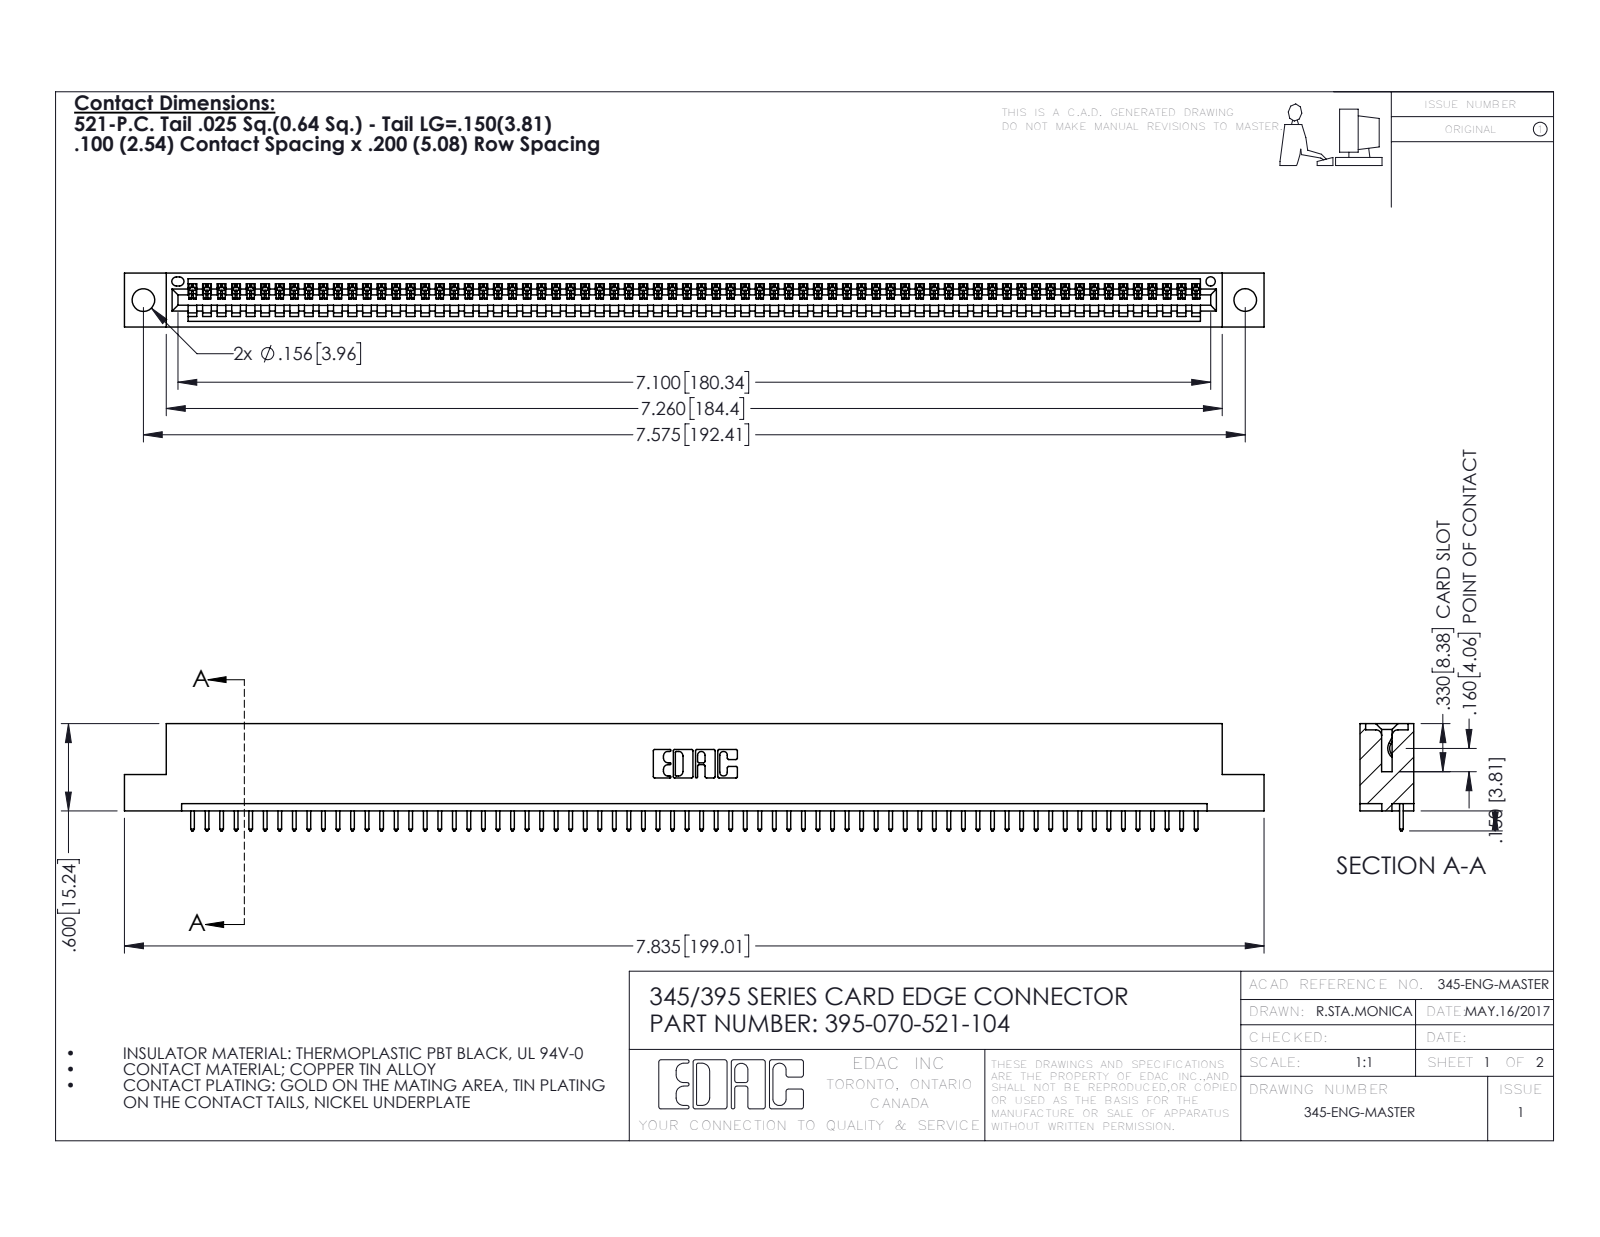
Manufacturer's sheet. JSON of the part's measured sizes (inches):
{"part_name": "345-292-001_345-293-121; 395-070-521-104; 345 Part_Flush Mounting Lugs - 0.156 Dia-TH", "step_written_by": "SolidWorks 2016 (CONFIG_CONTROL_DESIGN)", "units": "inches", "bodies": {"solids": 71, "faces": 4186, "planar": 2880, "cylindrical": 1306, "other": 0}, "overall_size": [7.835, 0.737, 0.37], "volume_in3": 1.15, "surface_area_in2": 37.9, "round_holes": [[0.156, 2], [0.064, 1]], "partial_cylinders_radius": [[0.006, 140], [0.01, 140], [0.01, 22], [0.007, 6], [0.031, 6], [0.026, 3], [0.031, 2], [0.04, 2]], "face_to_face_distances": [0.298, 0.072, 0.37, 0.2, 0.098, 0.272, 0.025, 0.225, 0.149, 0.072], "hole_center_spacings": [0.27, 7.339, 7.575]}
